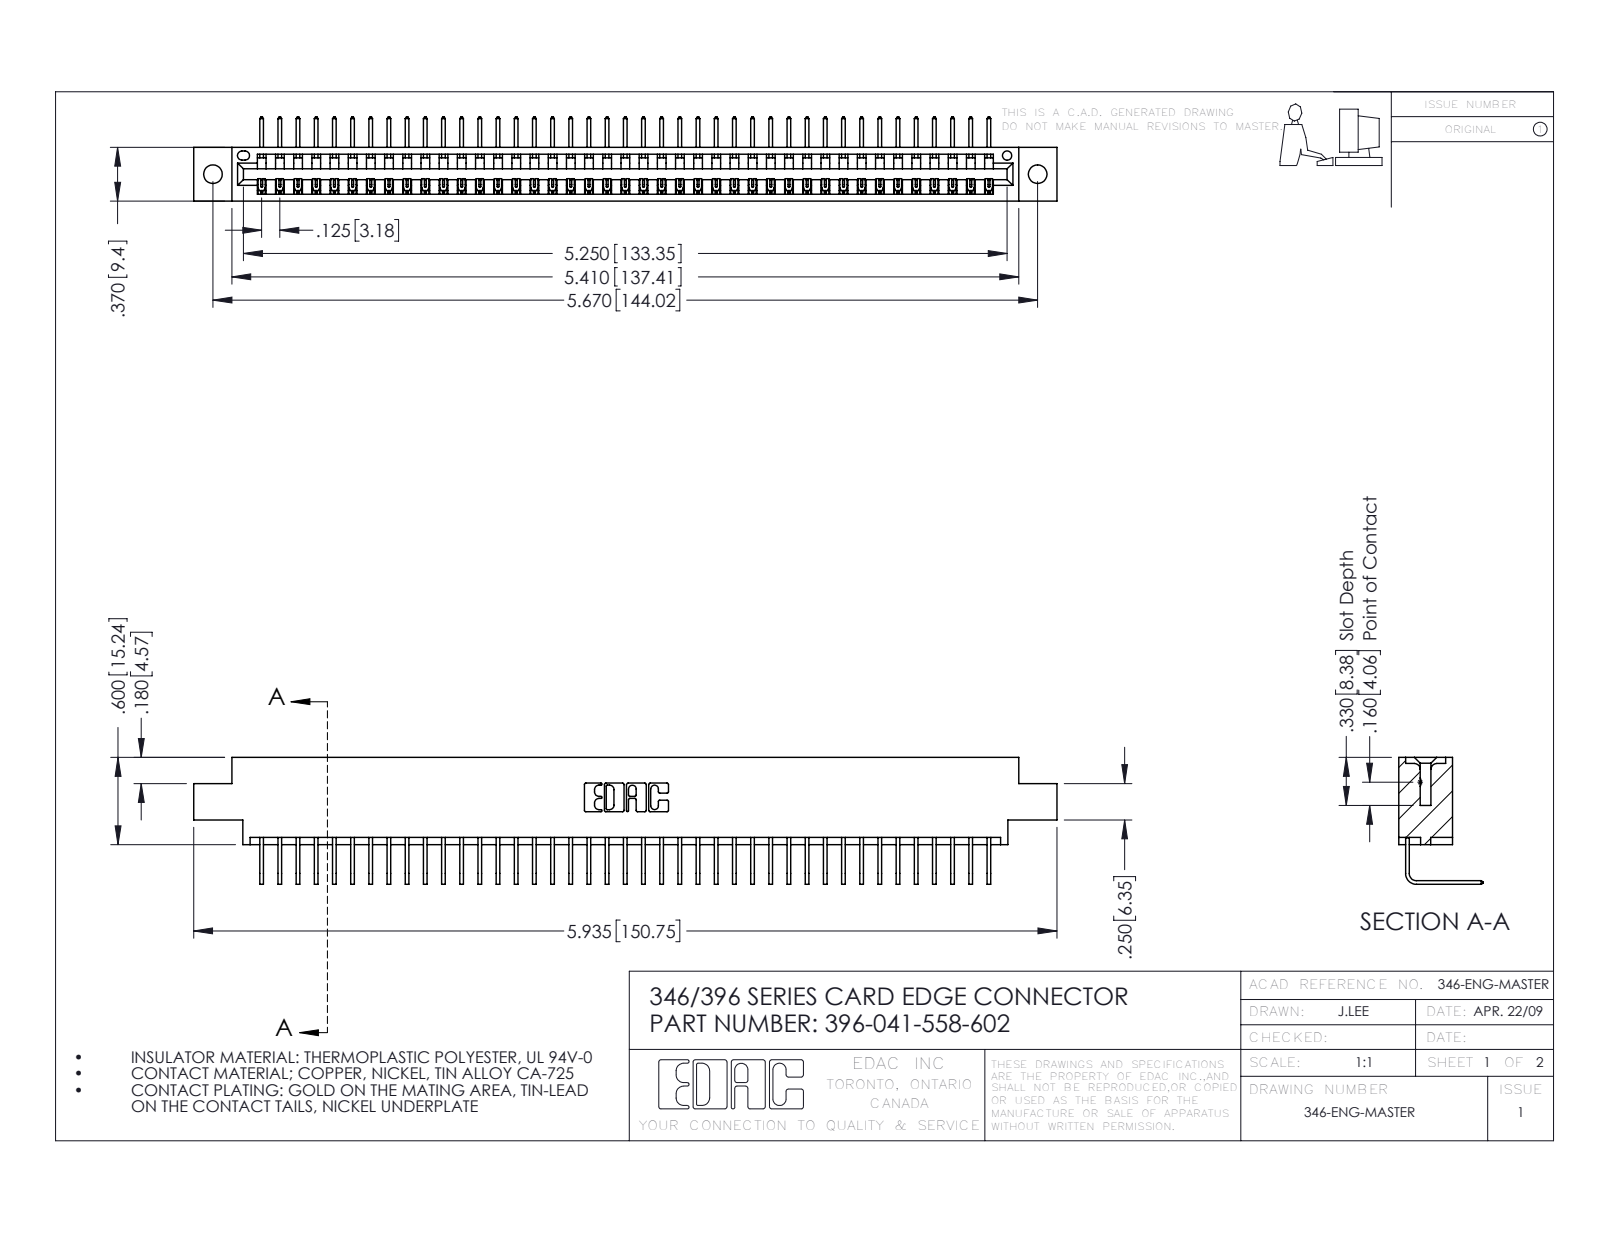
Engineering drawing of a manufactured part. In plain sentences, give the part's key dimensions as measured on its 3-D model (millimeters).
The part is named "345-292-001_558 Tail - 2; 346 Part_0.170 Offset - 0.128 Dia; 396-041-558-602". Its 3-D file was written by "SolidWorks 2016 (CONFIG_CONTROL_DESIGN)". It is 42 solids with 2586 faces: 1802 planar, 784 cylindrical and 0 other. Overall it measures 150.7 by 22.2 by 14.7 millimeters. Its volume is 14 400 cubic millimeters and its surface area 18 650 square millimeters. Round holes: 2 of diameter 3.3, 1 of diameter 1.6. Partial cylindrical surfaces (rounded edges, fillets, slot ends): 82 of radius 0.2, 22 of radius 0.3, 6 of radius 0.2, 6 of radius 0.8, 3 of radius 0.7, 2 of radius 0.8, 2 of radius 1, 1 of radius 0.4. The main face-to-face distances are 8.2, 1.2, 9.4, 6.4, 7.6, 0.6, 1.8, 3.8, 5.6, 2.5. The hole center spacings are 6.2, 138.7, 144.
